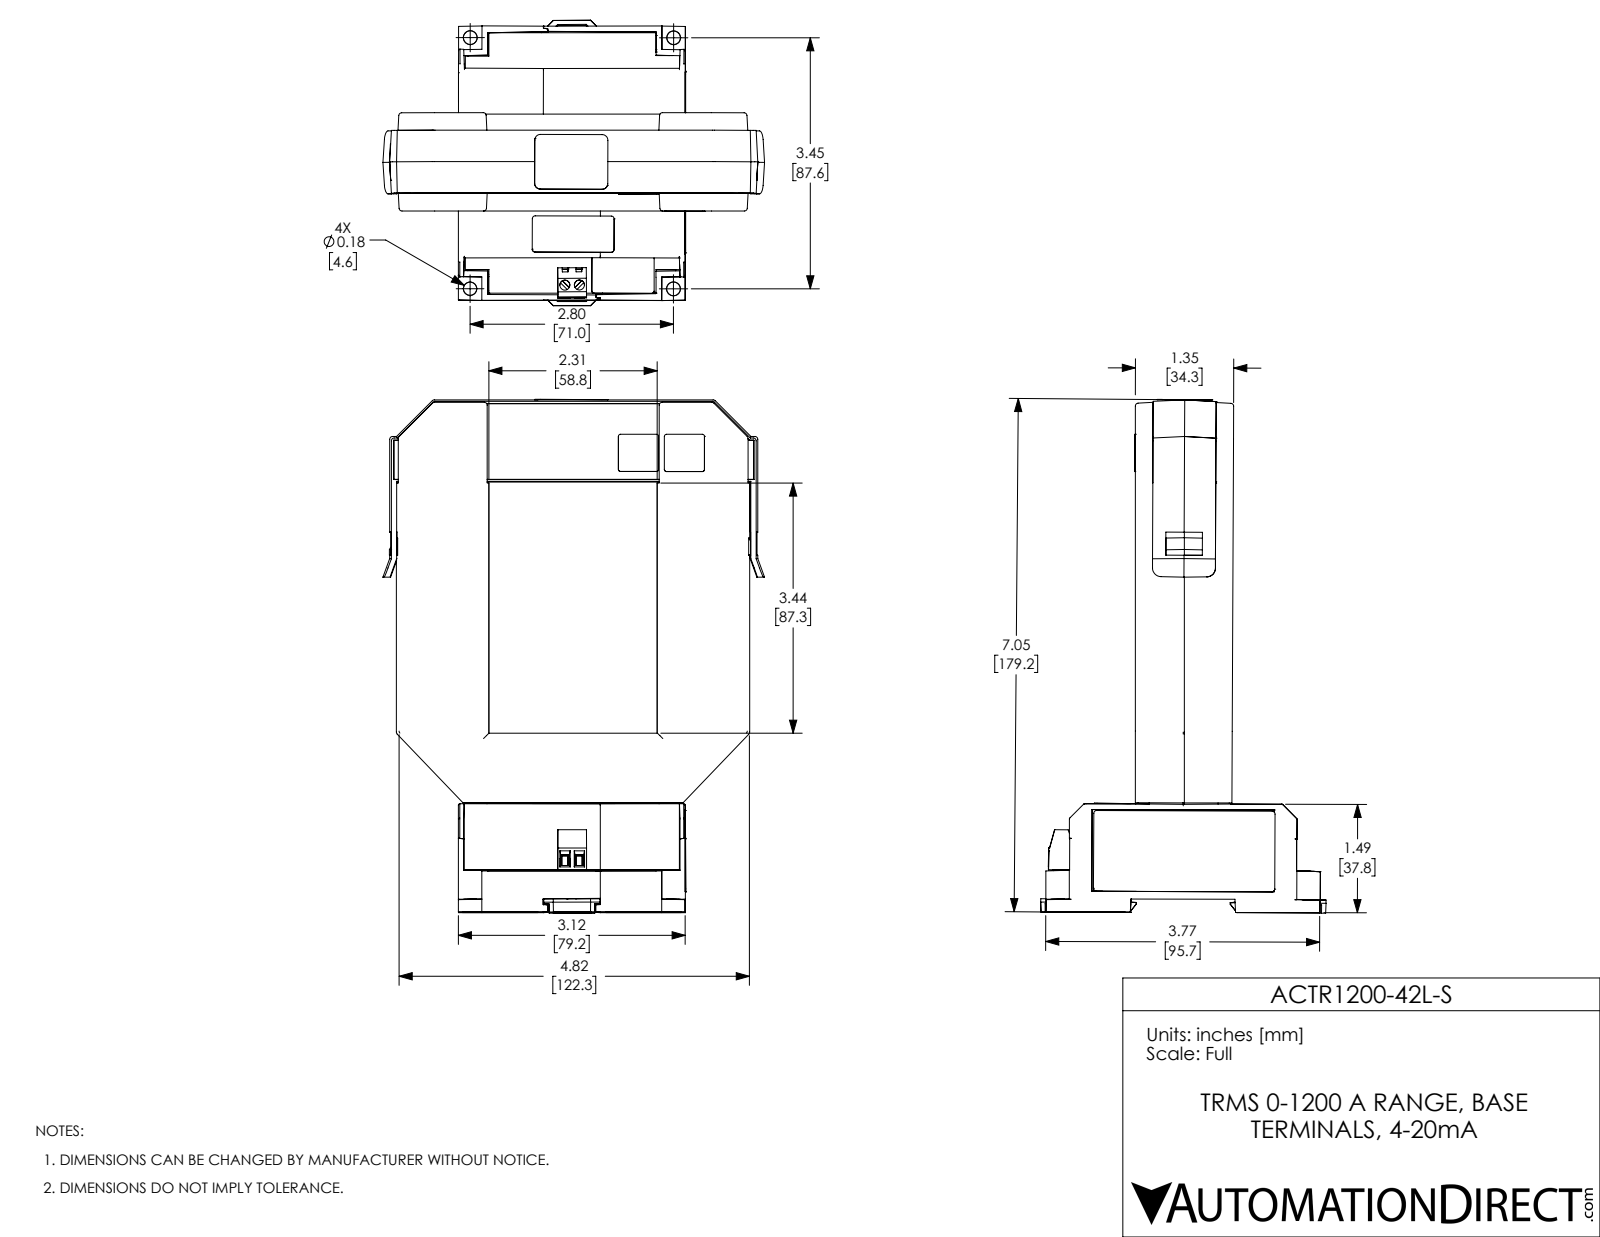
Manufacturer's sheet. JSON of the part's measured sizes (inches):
{"part_name": "ACTR1200-42L-S", "step_written_by": "SolidWorks 2017 (AUTOMOTIVE_DESIGN)", "units": "inches", "bodies": {"solids": 17, "faces": 1436, "planar": 1189, "cylindrical": 167, "other": 80}, "overall_size": [7.061, 5.246, 3.923], "volume_in3": 11.18, "surface_area_in2": 303.6, "round_holes": [[0.039, 4], [0.138, 2]], "round_bosses_or_shafts": [[0.197, 2], [0.118, 2]], "partial_cylinders_radius": [[0.04, 44], [0.02, 30], [0.03, 12], [0.039, 12], [0.004, 8], [0.079, 4], [0.129, 4], [0.119, 2]], "face_to_face_distances": [0.12, 0.059, 3.583, 0.08, 0.12, 0.239, 0.119, 3.028, 0.071, 0.904], "hole_center_spacings": [0.327, 0.547, 0.2, 0.22, 0.874]}
